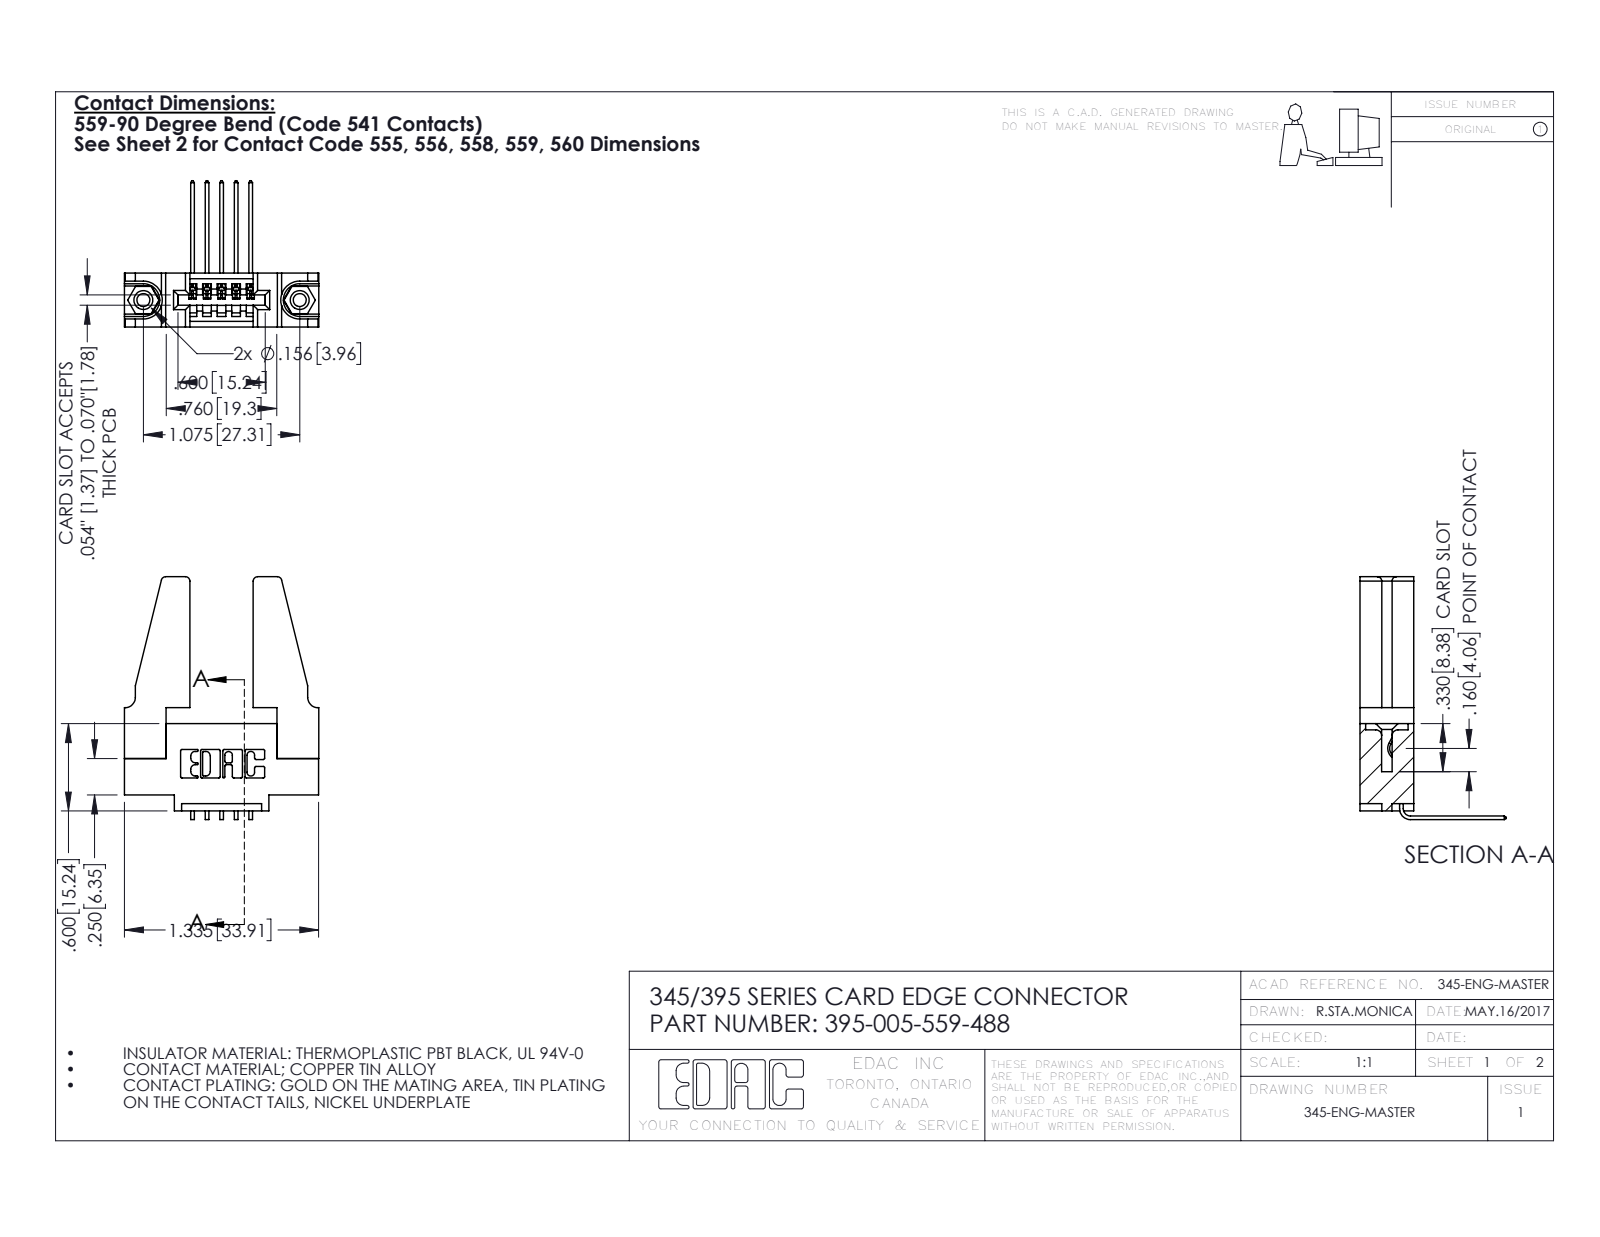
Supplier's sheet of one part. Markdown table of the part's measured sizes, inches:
| quantity | value |
| --- | --- |
| part name | 345 Part_0.110 Offset - 0.156 Dia-TH; 345-250-001_345-250-001-102; 345-292-001_558 559 Tail - 1; 345-220-078_345-220-088 (+1 more) |
| STEP written by | SolidWorks 2016 (CONFIG_CONTROL_DESIGN) |
| units | inches |
| bodies | 10 solids, 554 faces (366 planar, 172 cylindrical, 16 other) |
| overall size | 1.669 × 1.336 × 1.005 |
| volume | 0.373 in³ |
| surface area | 10.25 in² |
| round holes (diameter × count) | 0.089 × 2, 0.125 × 2, 0.156 × 2, 0.064 × 1 |
| round bosses / shafts (diameter × count) | 0.155 × 2 |
| partial cylindrical surfaces (radius × count) | 0.01 × 22, 0.006 × 10, 0.03 × 8, 0.007 × 6, 0.031 × 6, 0.026 × 3, 0.031 × 2, 0.04 × 2 |
| main face-to-face distances | 0.37, 0.072, 0.298, 0.2, 0.148, 0.15, 0.22, 0.077, 0.45, 0.598 |
| hole center spacings | 0.27, 0.847, 1.075 |
